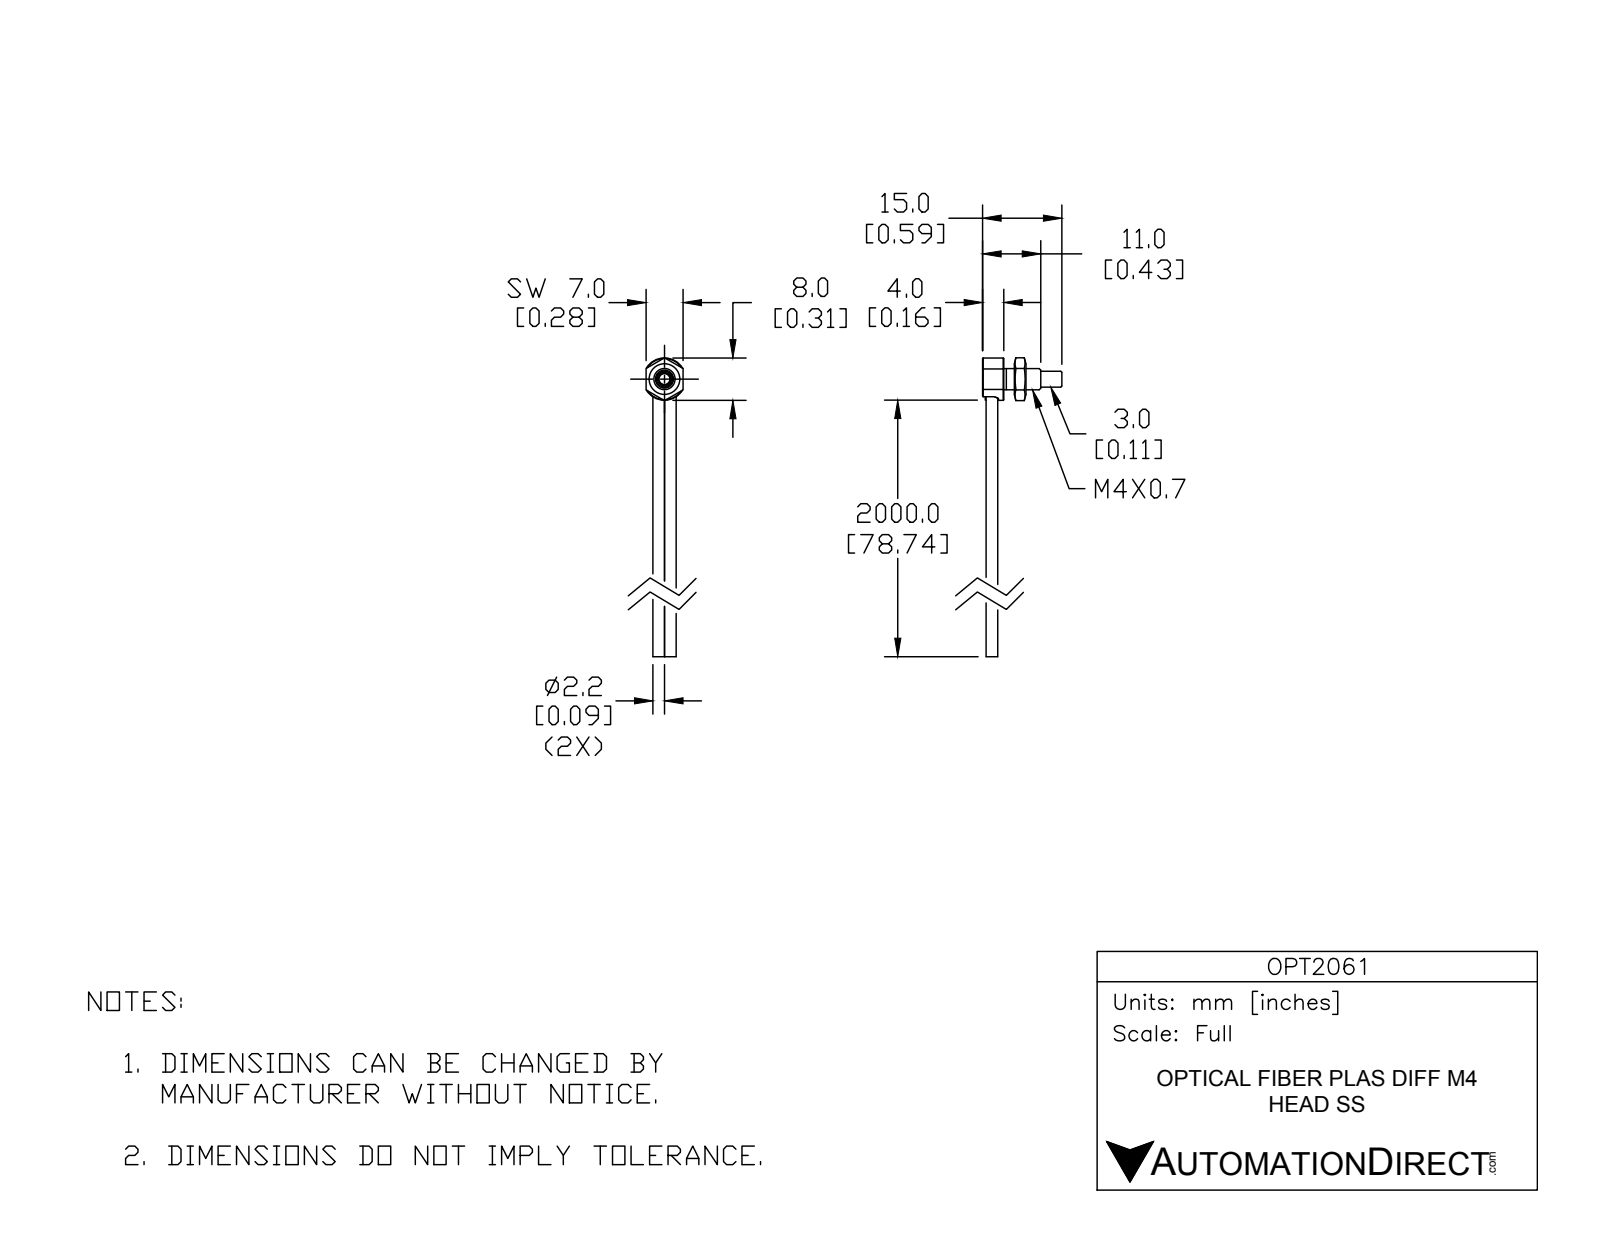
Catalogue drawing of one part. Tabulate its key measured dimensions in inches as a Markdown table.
| quantity | value |
| --- | --- |
| part name | OPT2061 |
| STEP written by | SolidWorks 2014 (AUTOMOTIVE_DESIGN) |
| units | inches |
| bodies | 1 solid, 58 faces (24 planar, 21 cylindrical, 13 other) |
| overall size | 2.226 × 0.591 × 0.276 |
| volume | 0.045 in³ |
| surface area | 1.644 in² |
| round holes (diameter × count) | 0.236 × 1 |
| round bosses / shafts (diameter × count) | 0.087 × 2, 0.157 × 1, 0.118 × 1 |
| partial cylindrical surfaces (radius × count) | 0.043 × 2, 0.156 × 1, 0.157 × 1 |
| main face-to-face distances | 0.276, 0.154, 0.157, 0.232, 0.319, 0.079, 0.165, 0.087, 0.236, 0.323 |
